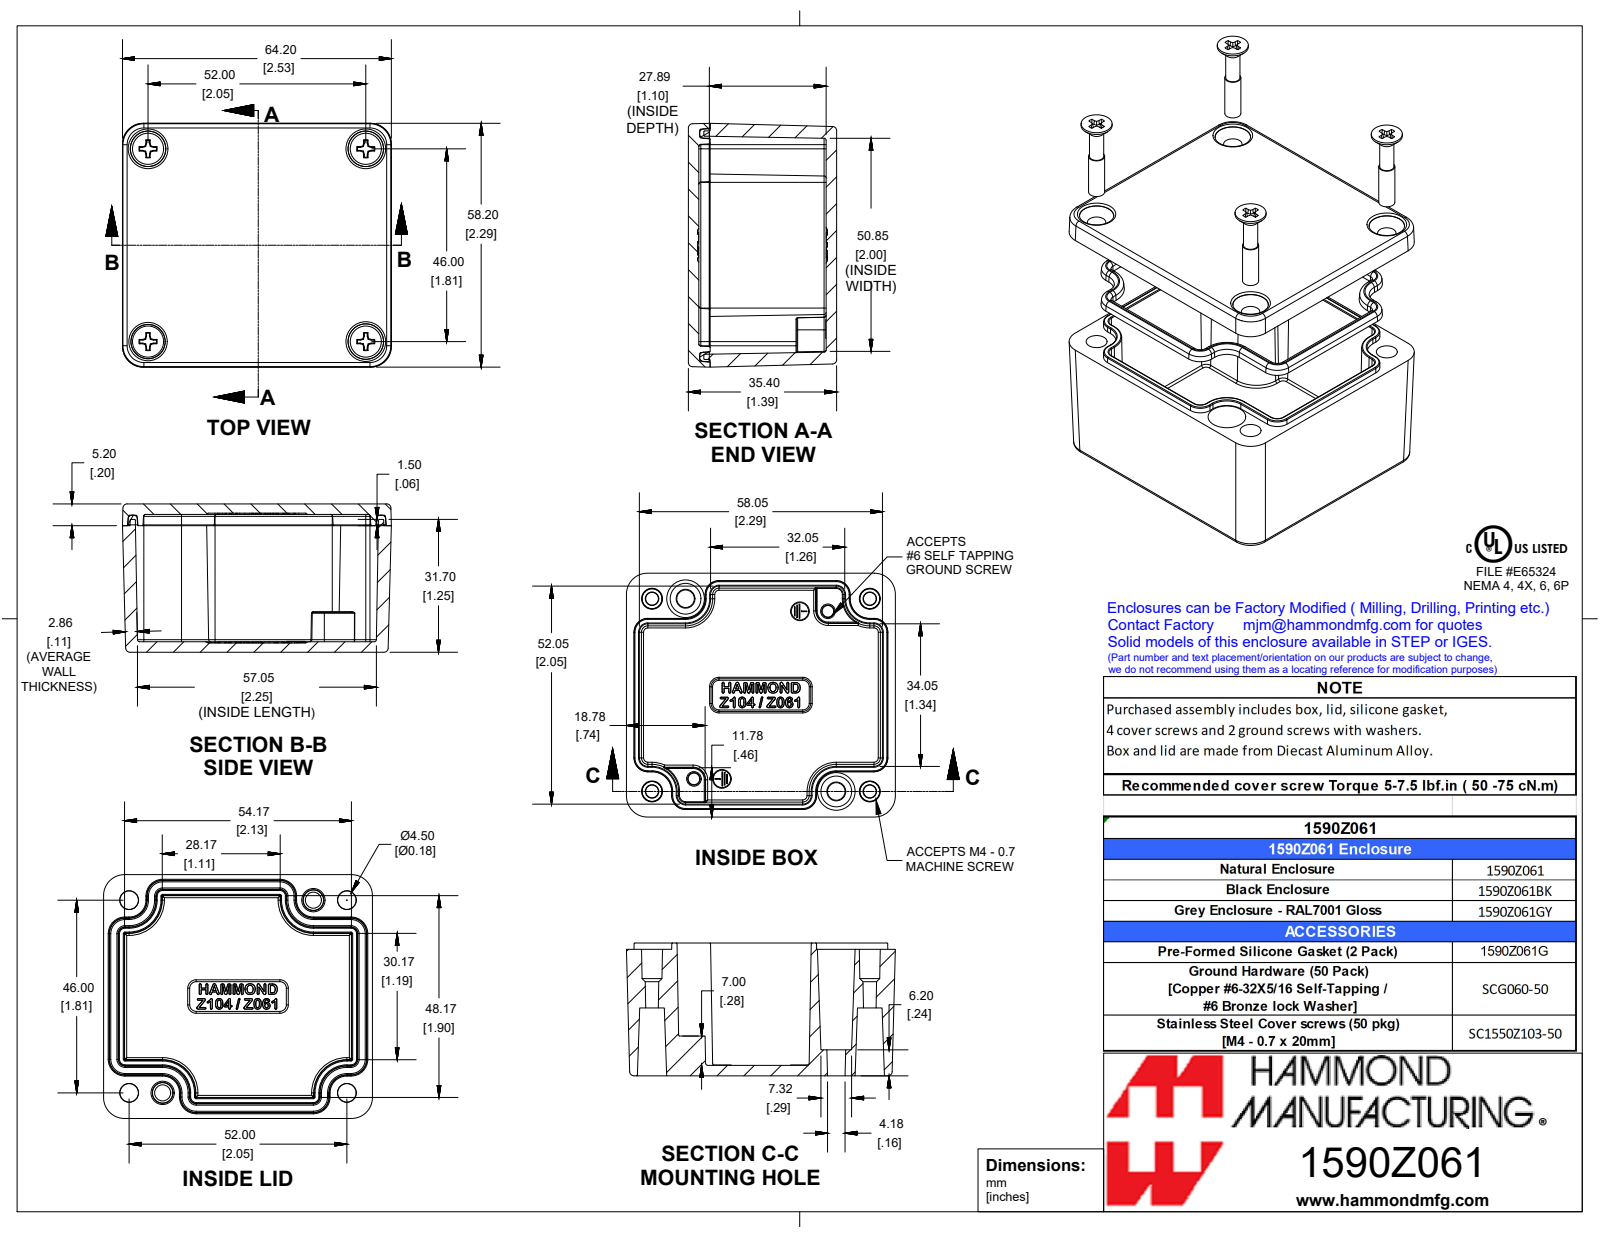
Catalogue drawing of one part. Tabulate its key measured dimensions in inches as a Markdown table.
| quantity | value |
| --- | --- |
| part name | 1590Z061BK |
| STEP written by | SolidWorks 2019 (CONFIG_CONTROL_DESIGN) |
| units | inches |
| bodies | 6 solids, 1097 faces (379 planar, 156 cylindrical, 562 other) |
| overall size | 2.528 × 2.291 × 1.394 |
| volume | 2.893 in³ |
| surface area | 54.45 in² |
| round bosses / shafts (diameter × count) | 0.15 × 4, 0.135 × 4 |
| partial cylindrical surfaces (radius × count) | 0.008 × 60, 0.02 × 34, 0.012 × 20, 0.039 × 8, 0.197 × 8 |
| main face-to-face distances | 0.098, 1.295, 1.394, 1.197, 1.189, 0.106, 1.091, 0.205, 0.354, 2.291 |
